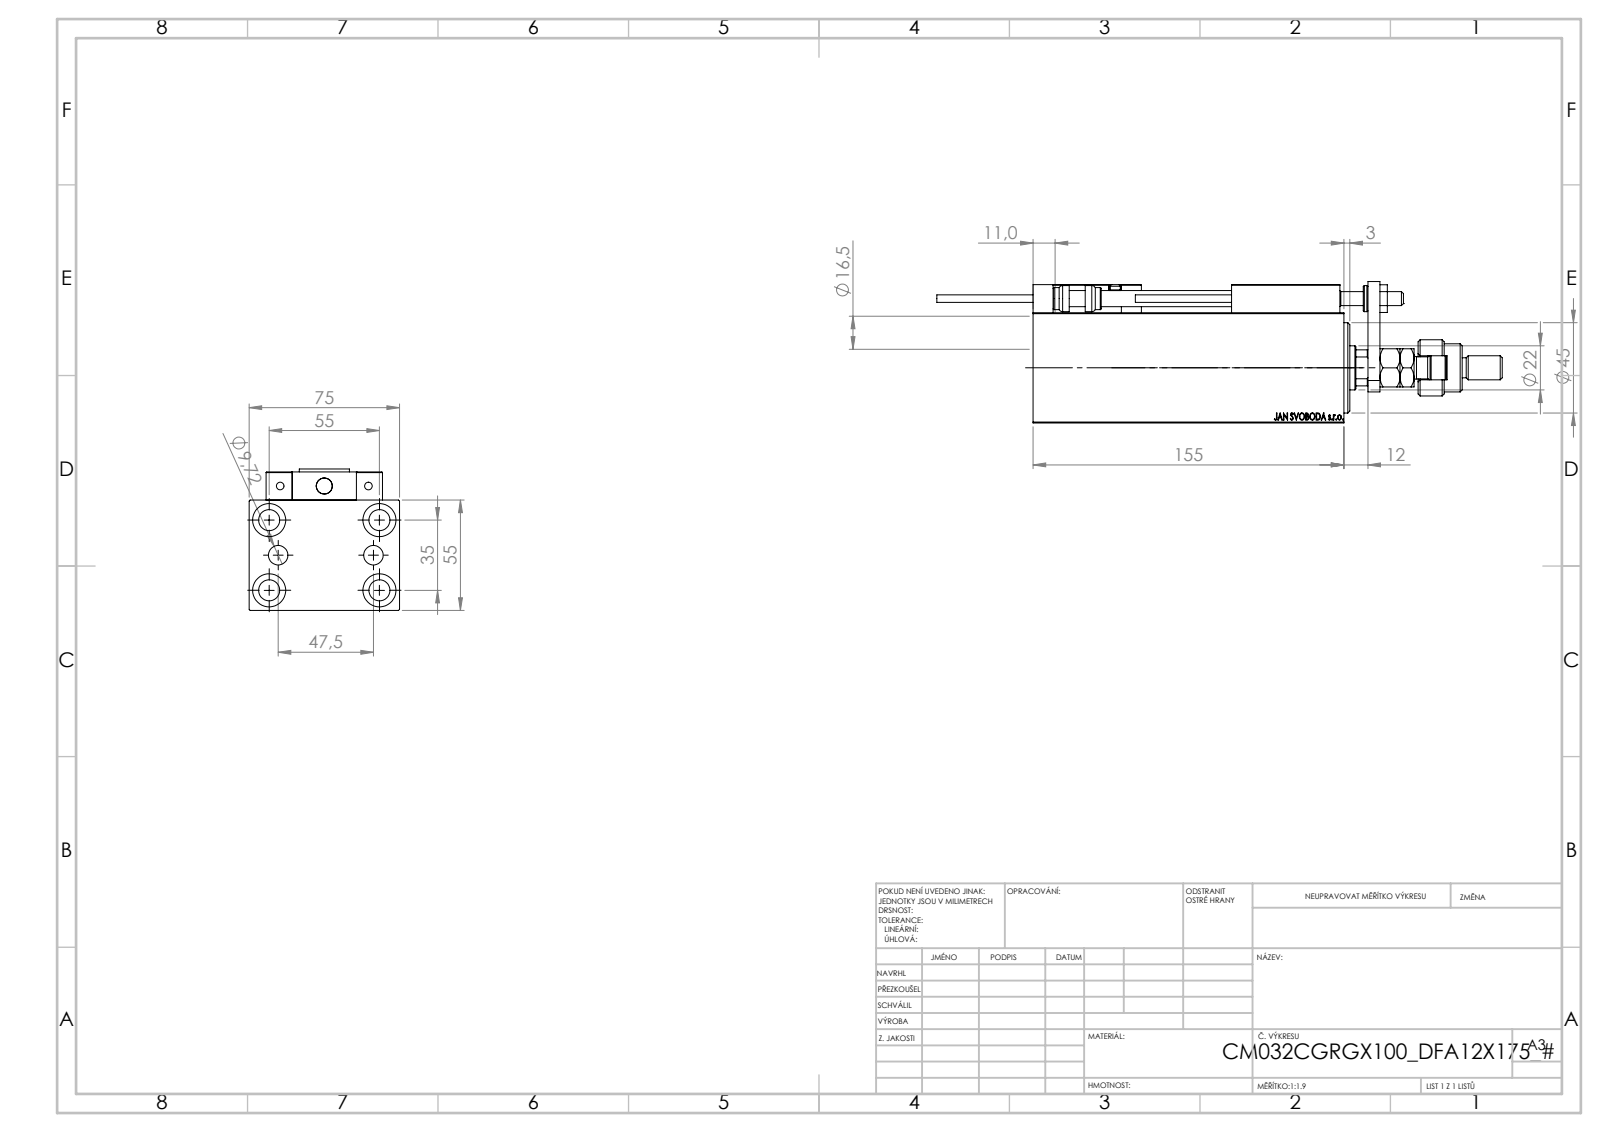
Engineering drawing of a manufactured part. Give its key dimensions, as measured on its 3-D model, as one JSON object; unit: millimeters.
{"part_name": "Block; V450CM_C_Body; MFA; KONCOVKA (+8 more)", "step_written_by": "SolidWorks 2019 (CONFIG_CONTROL_DESIGN)", "units": "millimeters", "bodies": {"solids": 25, "faces": 1363, "planar": 588, "cylindrical": 197, "other": 578}, "overall_size": [282, 75, 70.5], "volume_mm3": 602216, "surface_area_mm2": 137272, "round_holes": [[4, 6], [8, 5], [10.5, 5], [16.5, 5], [3.2, 4], [5, 2], [9.72, 2], [7, 1], [22, 1], [25.5, 1], [32, 1], [34, 1]], "round_bosses_or_shafts": [[11, 2], [5, 2], [3.8, 2], [28, 1], [24, 1], [18, 1], [13, 1], [12, 1]], "partial_cylinders_radius": [[0.3, 30], [3, 2], [9.75, 1], [10.5, 1]], "face_to_face_distances": [55, 75, 14, 5, 69, 18, 25, 6, 12, 10], "hole_center_spacings": [17.9, 32.6, 54.16, 11.37, 20, 23.75, 29.59, 29.69]}
